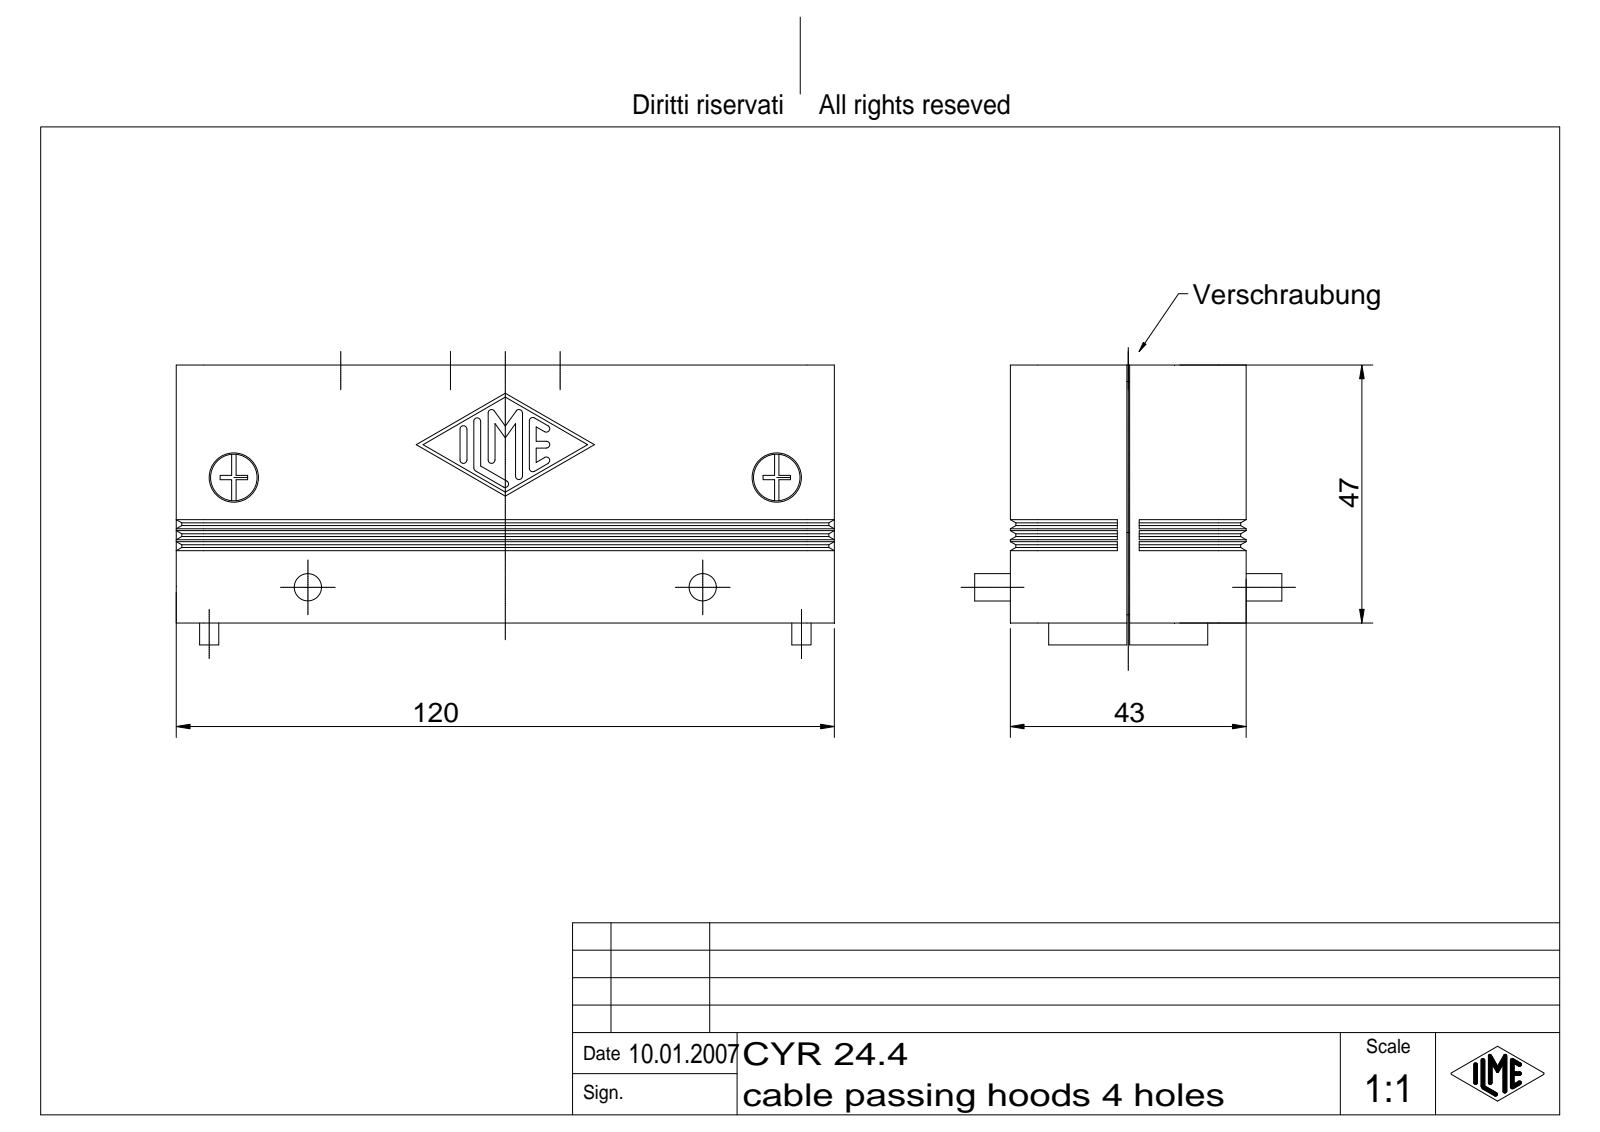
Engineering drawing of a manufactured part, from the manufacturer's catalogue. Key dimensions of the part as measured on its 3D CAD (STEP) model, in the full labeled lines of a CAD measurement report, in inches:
Part name (STEP PRODUCT): CYR 24.4
STEP written by: Autodesk Inventor 7 (AUTOMOTIVE_DESIGN)
Units: inches
Bodies: 4 solids, 433 faces (246 planar, 118 cylindrical, 69 other)
Overall size (bounding box): 4.724 × 2.205 × 2.008
Volume: 7.968 in³ · Surface area: 97.08 in²
Round holes (diameter × count): ⌀0.197 ×4, ⌀0.394 ×4, ⌀0.63 ×4, ⌀0.669 ×4, ⌀0.748 ×4, ⌀0.354 ×2
Round bosses / shafts (diameter × count): ⌀0.512 ×4, ⌀0.295 ×4, ⌀0.335 ×2, ⌀0.197 ×2
Partial cylindrical surfaces — rounded edges, fillets, slot ends (radius × count): R0.024 ×14, R0.039 ×4, R0.079 ×4, R0.197 ×4, R0.157 ×2, R0.472 ×2, R0.492 ×2
Main face-to-face distances: 0.118, 1.575, 0.157, 1.693, 0.02, 0.925, 1.201, 0.719, 1.457, 0.276
Hole centre spacings: 0.787, 1.575, 2.362, 3.898
